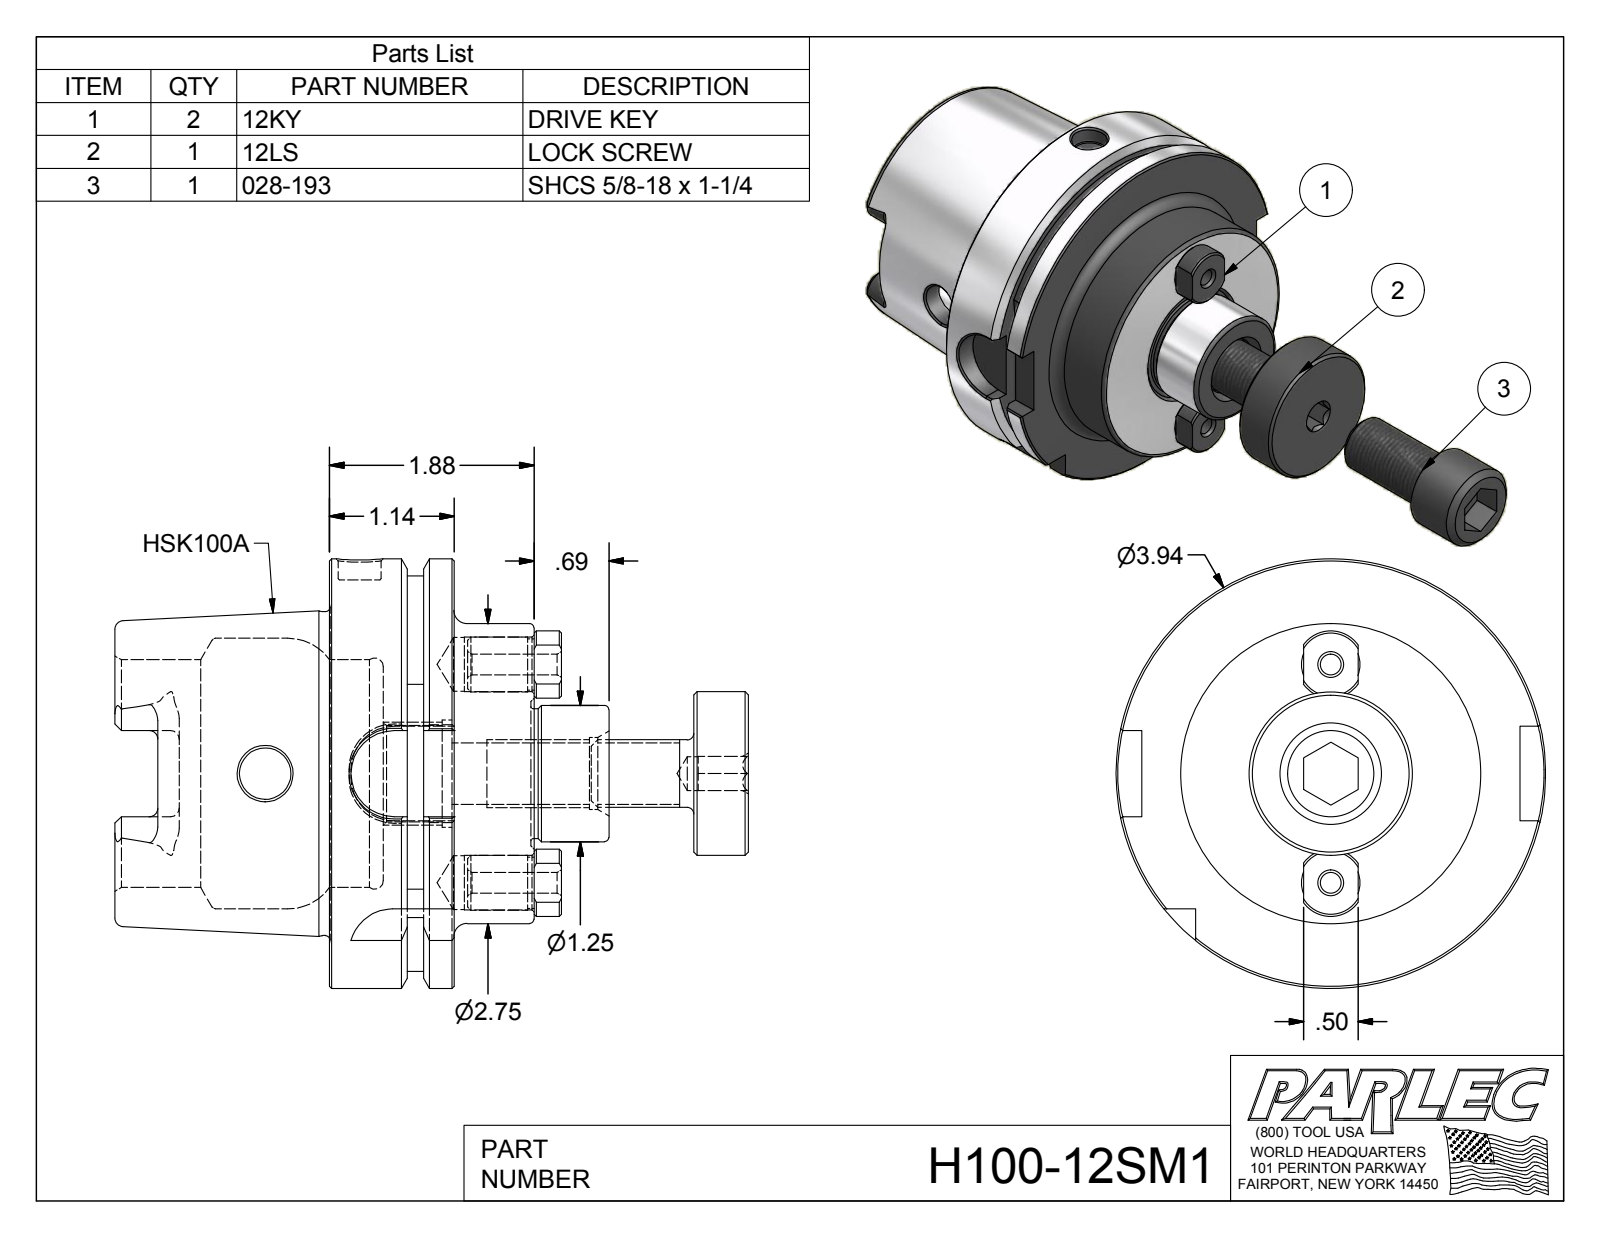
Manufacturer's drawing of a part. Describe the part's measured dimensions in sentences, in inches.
The part is named "H100-12SM1; 12KY; 12LS; 028-193". Its 3-D file was written by "Autodesk Inventor 2012 (AUTOMOTIVE_DESIGN)". It is 5 solids with 210 faces: 79 planar, 54 cylindrical and 77 other. Overall it measures 8.331 by 3.937 by 3.937 inches. Its volume is 22.16 cubic inches and its surface area 109.4 square inches. Round holes: 2 of diameter 0.19, 2 of diameter 0.493, 2 of diameter 0.5, 1 of diameter 0.312, 1 of diameter 0.394, 1 of diameter 0.472, 1 of diameter 0.565, 1 of diameter 0.66, 1 of diameter 0.881, 1 of diameter 0.985, 1 of diameter 2.087, 1 of diameter 2.48. Round bosses or shafts: 2 of diameter 0.505, 2 of diameter 0.47, 1 of diameter 3.937, 1 of diameter 2.967, 1 of diameter 2.75, 1 of diameter 1.5, 1 of diameter 1.25, 1 of diameter 1.19. Partial cylindrical surfaces (rounded edges, fillets, slot ends): 6 of radius 0.079, 4 of radius 0.192, 4 of radius 0.394, 2 of radius 0.308, 1 of radius 1.811. The main face-to-face distances are 1.142, 1.875, 0.733, 0.492, 0.65, 1.383, 3.838, 3.346, 2.696, 1.963. The hole center spacings are 1, 2.
